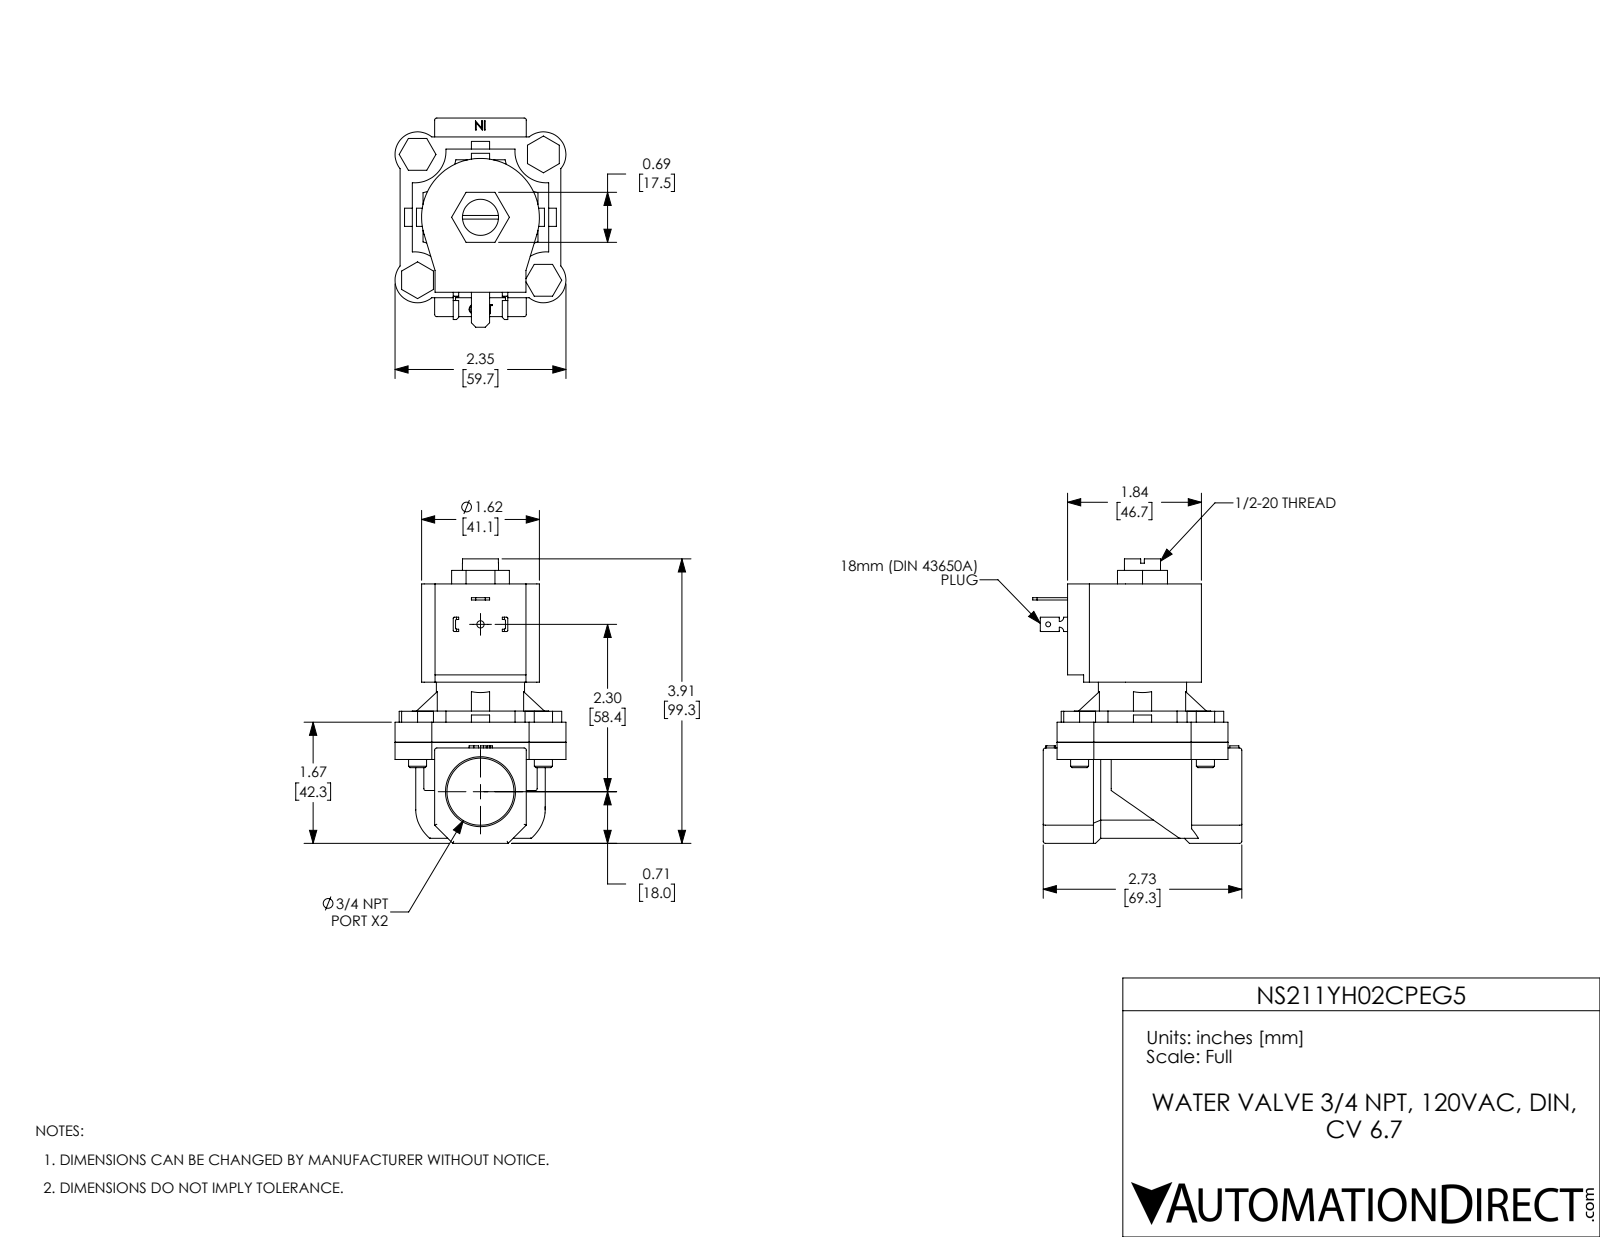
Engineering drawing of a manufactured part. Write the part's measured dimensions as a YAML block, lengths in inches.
part_name: "NS211YH02CPEG5"
step_written_by: "SolidWorks 2024 (CONFIG_CONTROL_DESIGN)"
units: inches
bodies: {solids: 11, faces: 387, planar: 241, cylindrical: 113, other: 33}
overall_size: [3.91, 2.875, 2.35]
volume: 9.997
surface_area: 68.35
round_holes:
  - {diameter: 0.25, count: 4}
  - {diameter: 0.067, count: 1}
  - {diameter: 0.1, count: 1}
  - {diameter: 0.496, count: 1}
  - {diameter: 0.512, count: 1}
  - {diameter: 0.922, count: 1}
  - {diameter: 1.155, count: 1}
round_bosses_or_shafts:
  - {diameter: 0.248, count: 4}
  - {diameter: 1.213, count: 1}
partial_cylinders:
  - {radius: 0.03, count: 15}
  - {radius: 0.015, count: 8}
  - {radius: 0.31, count: 4}
  - {radius: 0.432, count: 4}
  - {radius: 0.579, count: 4}
  - {radius: 0.06, count: 2}
  - {radius: 0.81, count: 1}
  - {radius: 0.89, count: 1}
face_to_face_distances: [0.276, 2.177, 1.901, 0.236, 0.512, 2.413, 1.063, 0.827, 0.551, 1.35]
hole_center_spacings: [1.223, 1.73, 2.446, 2.3]
